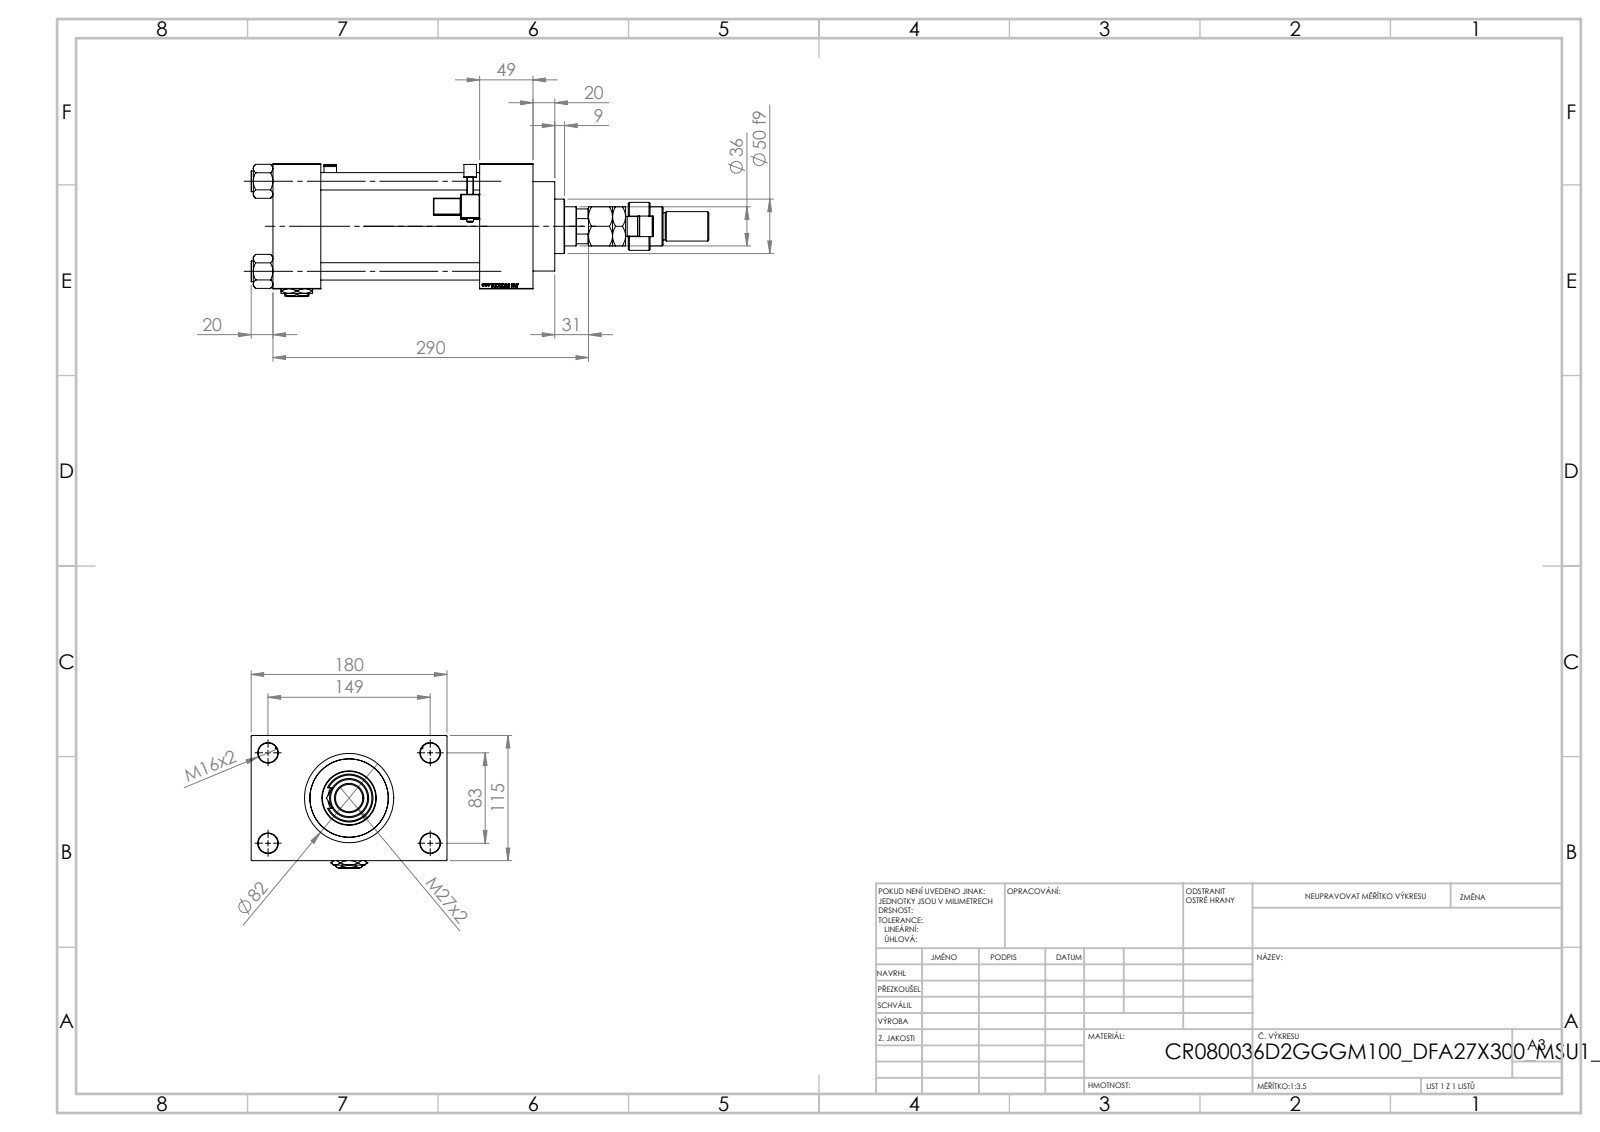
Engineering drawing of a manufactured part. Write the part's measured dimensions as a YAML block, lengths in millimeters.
part_name: "NUT_M5_D; FEMALE_PART_FOR_DFA; V215_VC_A; MFA (+5 more)"
step_written_by: "SolidWorks 2019 (CONFIG_CONTROL_DESIGN)"
units: millimeters
bodies: {solids: 16, faces: 1444, planar: 655, cylindrical: 169, other: 620}
overall_size: [420.5, 180, 122]
volume: 2342000
surface_area: 398114
round_holes:
  - {diameter: 16, count: 4}
  - {diameter: 18, count: 4}
  - {diameter: 7, count: 2}
  - {diameter: 26.44, count: 2}
  - {diameter: 35, count: 2}
  - {diameter: 25.5, count: 1}
  - {diameter: 39, count: 1}
  - {diameter: 61, count: 1}
  - {diameter: 72, count: 1}
  - {diameter: 80, count: 1}
round_bosses_or_shafts:
  - {diameter: 19, count: 4}
  - {diameter: 6, count: 2}
  - {diameter: 86, count: 1}
  - {diameter: 82, count: 1}
  - {diameter: 50, count: 1}
  - {diameter: 44, count: 1}
  - {diameter: 36, count: 1}
  - {diameter: 28, count: 1}
partial_cylinders:
  - {radius: 0.5, count: 48}
  - {radius: 1, count: 2}
  - {radius: 2.5, count: 2}
  - {radius: 4, count: 2}
  - {radius: 9.5, count: 1}
  - {radius: 15, count: 1}
  - {radius: 17.5, count: 1}
face_to_face_distances: [115, 146, 195, 49, 44, 190, 239, 32.5, 147.5, 180]
hole_center_spacings: [33.15, 58.48, 82.7, 85.28, 89.24, 115.85, 142.43, 83]
